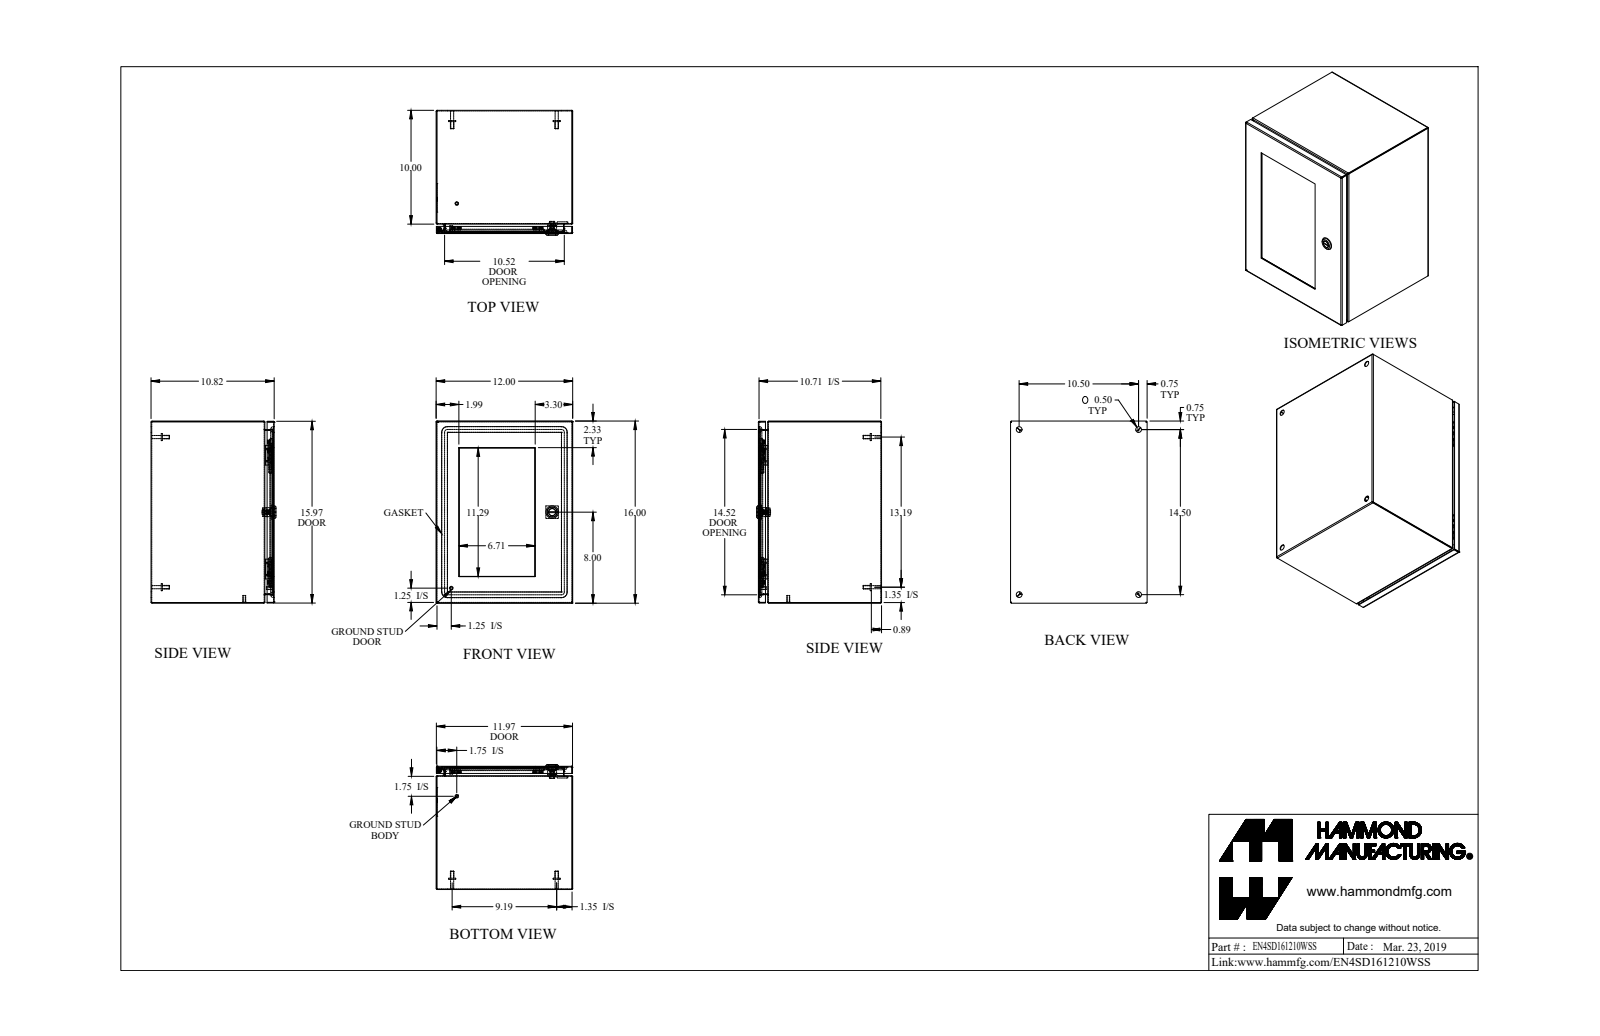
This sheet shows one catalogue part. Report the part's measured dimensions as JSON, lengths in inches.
{"part_name": "EN4SD161210WSS_Default", "step_written_by": "SolidWorks 2019 (CONFIG_CONTROL_DESIGN)", "units": "inches", "bodies": {"solids": 51, "faces": 1083, "planar": 544, "cylindrical": 327, "other": 212}, "overall_size": [16, 12, 10.982], "volume_in3": 86.25, "surface_area_in2": 2388, "round_holes": [[0.13, 10], [0.25, 10], [0.5, 5], [0.172, 1], [0.197, 1], [0.24, 1], [0.242, 1], [0.387, 1], [0.63, 1], [0.768, 1]], "round_bosses_or_shafts": [[0.226, 11], [0.368, 10], [0.164, 10], [0.313, 6], [0.625, 5], [0.275, 4], [0.25, 2], [1.1, 1]], "partial_cylinders_radius": [[0.029, 21], [0.086, 21], [0.188, 12], [0.125, 10], [0.006, 4], [0.016, 4], [0.062, 4], [0.088, 4]], "face_to_face_distances": [0.057, 11.943, 10.765, 15.943, 10.708, 11.886, 12, 15.886, 16, 0.25], "hole_center_spacings": [5.437, 5.438, 10.875, 0.894, 0.895, 6.188, 6.189, 7.225]}
